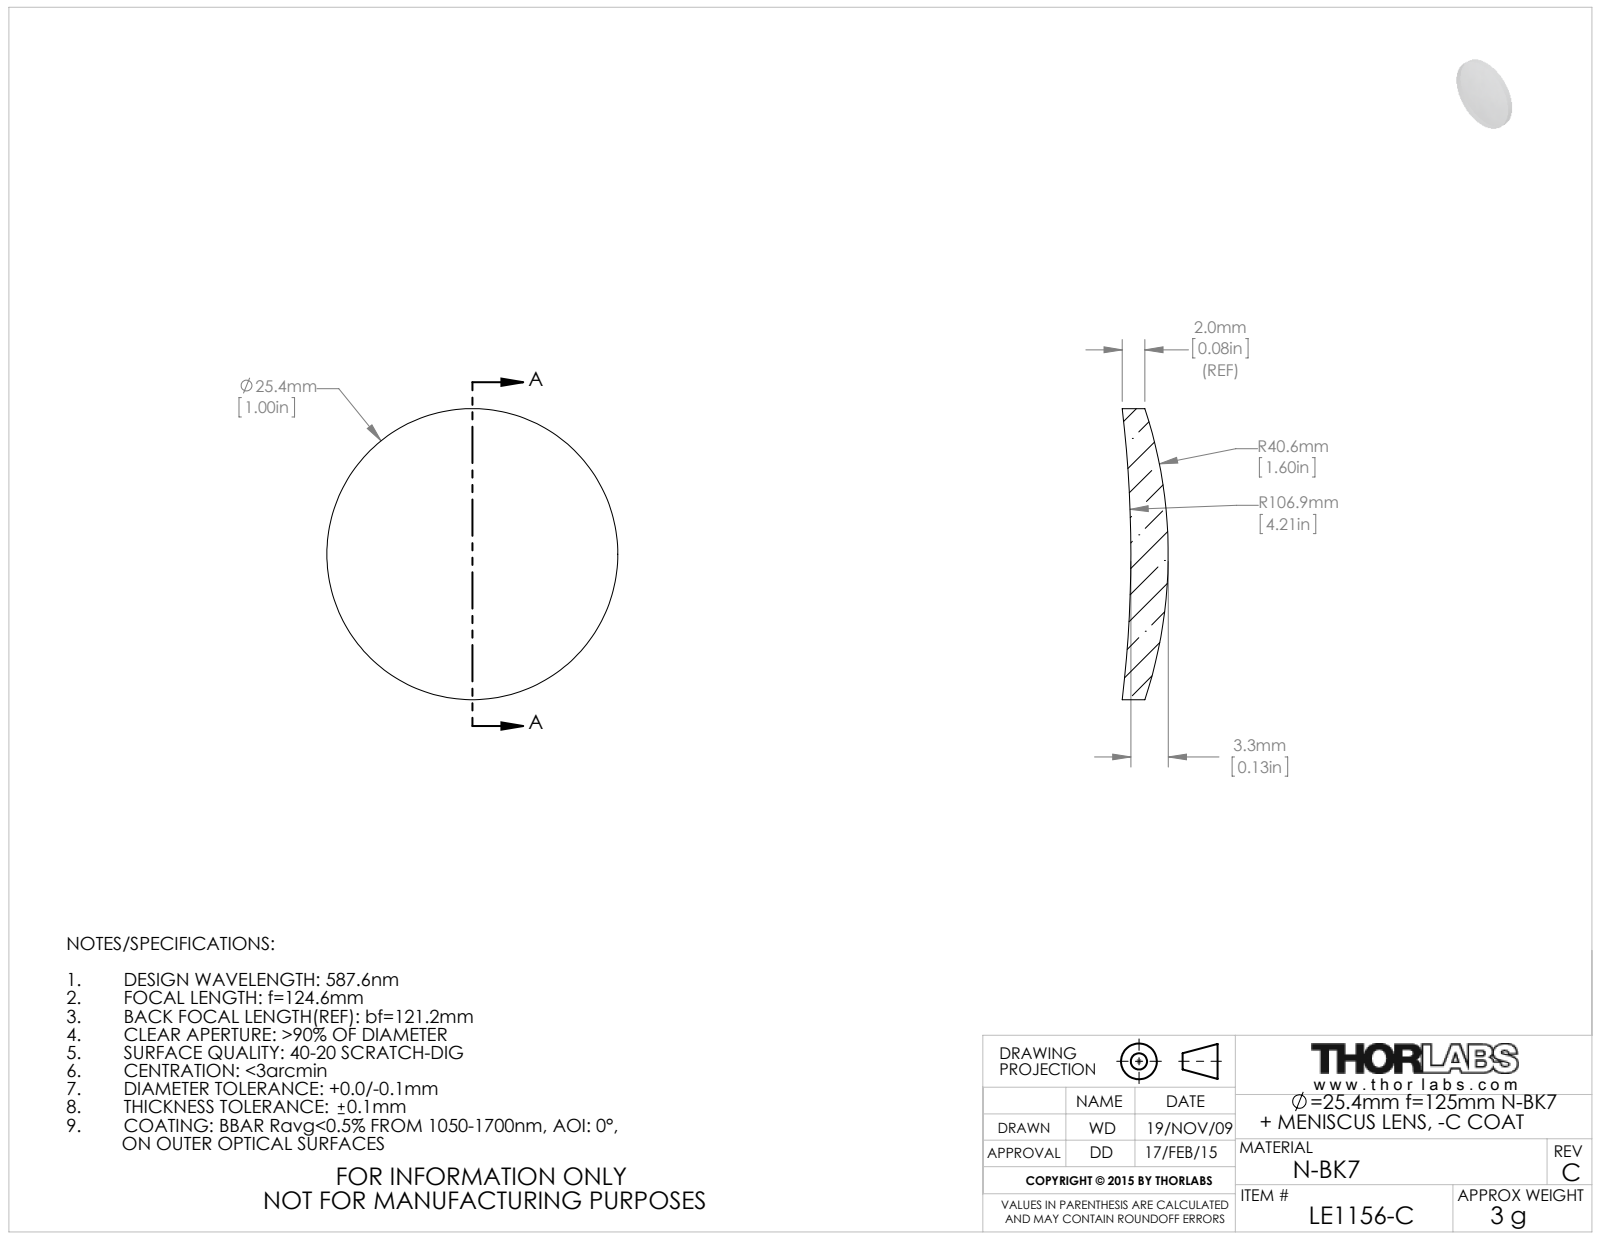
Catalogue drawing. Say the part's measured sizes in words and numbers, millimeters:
The part is named "4851-E0W". Its 3-D file was written by "SolidWorks 2009 (AUTOMOTIVE_DESIGN)". It is 1 solid with 6 faces: 0 planar, 2 cylindrical and 4 other. Overall it measures 25.4 by 25.4 by 4.02 millimeters. Its volume is 1 332 cubic millimeters and its surface area 1 186 square millimeters. Round bosses or shafts: 1 of diameter 25.4.
